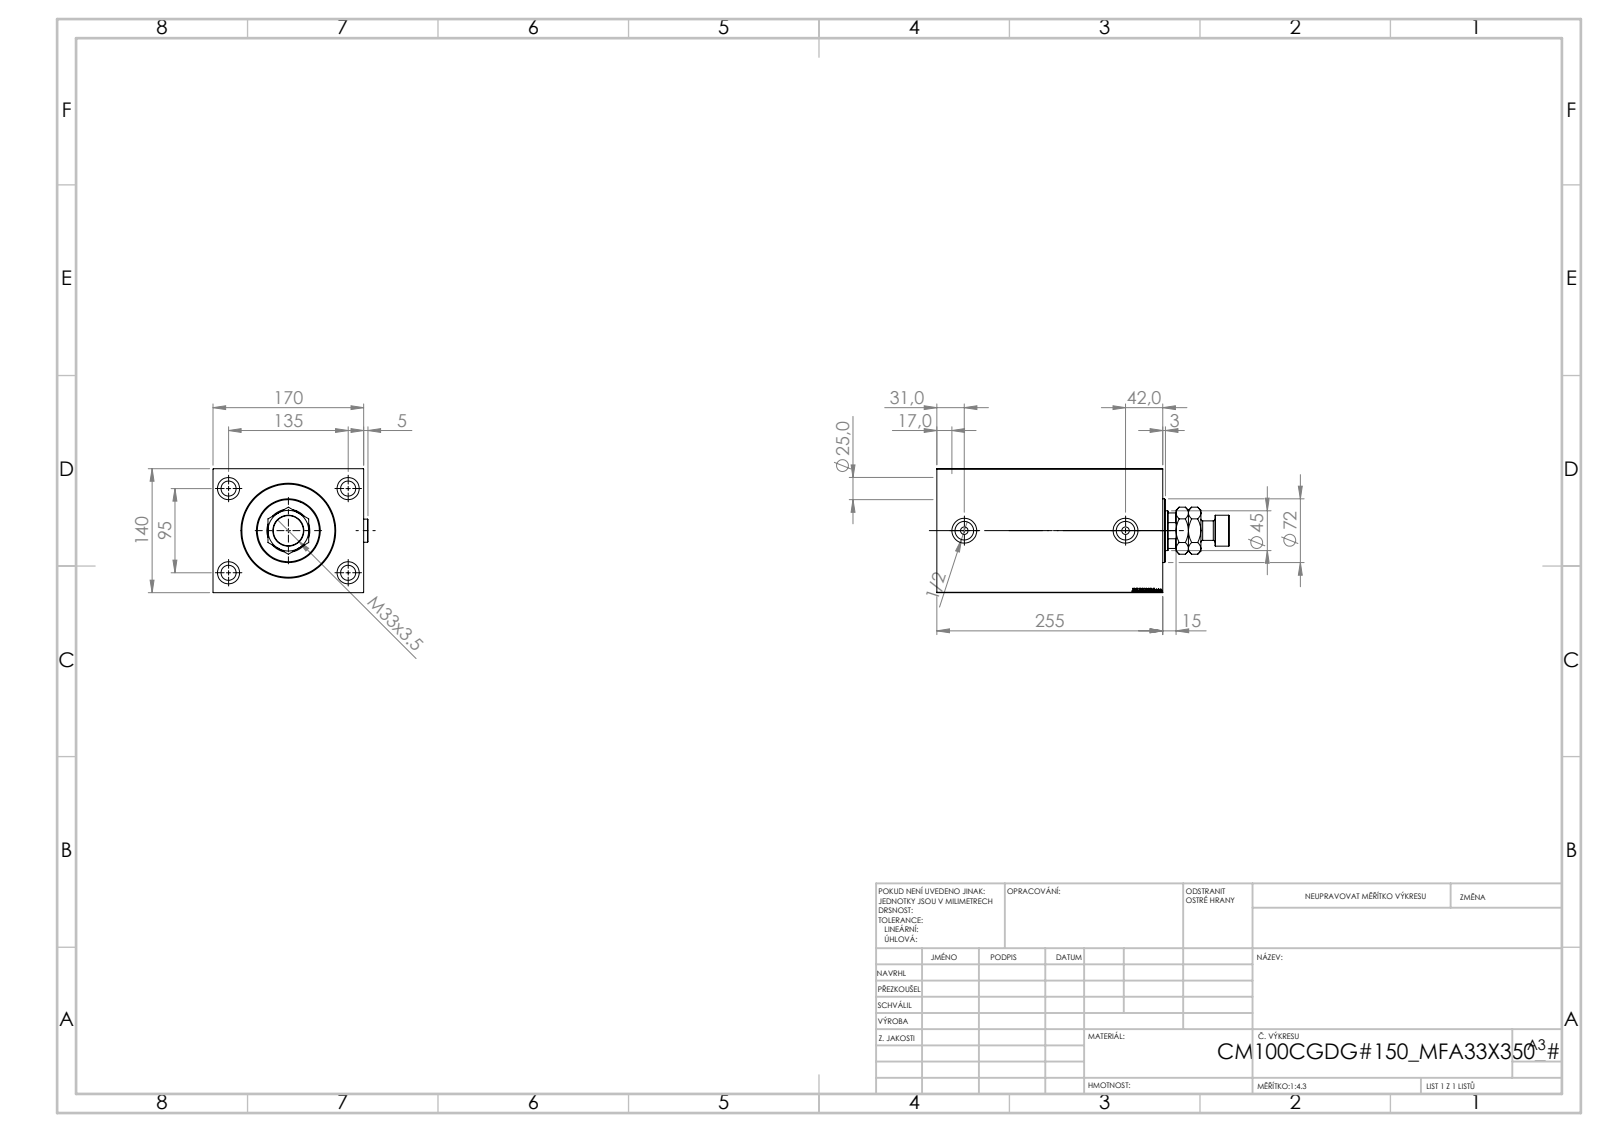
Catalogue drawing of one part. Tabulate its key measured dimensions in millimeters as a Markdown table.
| quantity | value |
| --- | --- |
| part name | V450CM_VC_B; V450CM_C_Body; Zatka_OIL_PORT; MFA (+1 more) |
| STEP written by | SolidWorks 2019 (CONFIG_CONTROL_DESIGN) |
| units | millimeters |
| bodies | 6 solids, 971 faces (459 planar, 82 cylindrical, 430 other) |
| overall size | 330 × 174.9 × 140 |
| volume | 4 913 000 mm³ |
| surface area | 440 885 mm² |
| round holes (diameter × count) | 17 × 4, 25 × 4, 8.5 × 2, 20.96 × 2, 28 × 2, 31.5 × 1, 45 × 1, 48.5 × 1, 100 × 1, 102 × 1, 105 × 1 |
| round bosses / shafts (diameter × count) | 26 × 2, 72 × 1, 35 × 1, 22 × 1 |
| partial cylindrical surfaces (radius × count) | 22 × 1 |
| main face-to-face distances | 140, 170, 255, 229, 26, 15, 240, 90, 214, 64 |
| hole center spacings | 82.54, 95, 135, 165.08, 182 |
